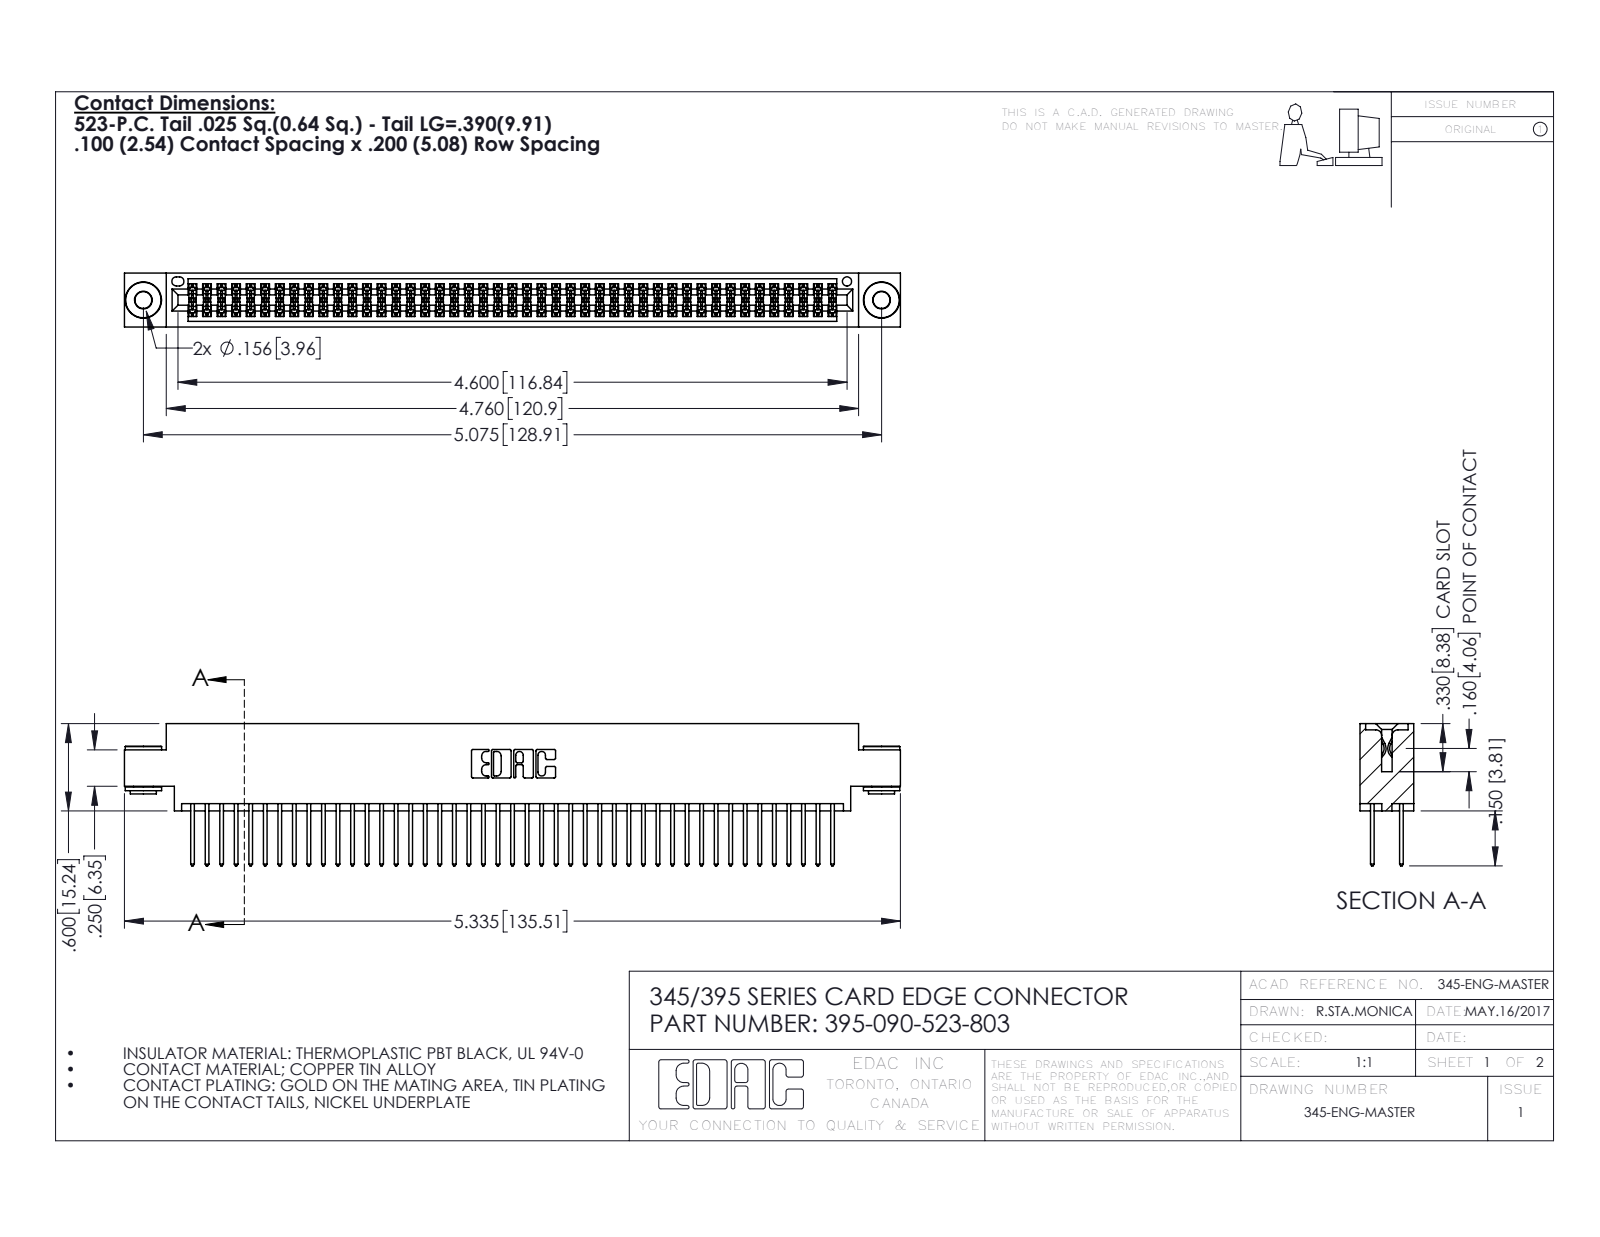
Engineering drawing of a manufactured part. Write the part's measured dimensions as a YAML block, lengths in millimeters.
part_name: "345-292-001_345-293-123; 345 Part_0.170 Offset - 0.156 Dia-TH; 395-090-523-803; 345-250-002_345-250-002-102"
step_written_by: "SolidWorks 2016 (CONFIG_CONTROL_DESIGN)"
units: millimeters
bodies: {solids: 93, faces: 4668, planar: 3064, cylindrical: 1596, other: 8}
overall_size: [135.5, 24.8, 9.4]
volume: 13300
surface_area: 20860
round_holes:
  - {diameter: 2.9, count: 2}
  - {diameter: 4, count: 2}
  - {diameter: 1.6, count: 1}
round_bosses_or_shafts:
  - {diameter: 6.4, count: 2}
  - {diameter: 4.6, count: 2}
  - {diameter: 3.5, count: 2}
partial_cylinders:
  - {radius: 0.2, count: 135}
  - {radius: 0.3, count: 90}
  - {radius: 0.3, count: 22}
  - {radius: 0.2, count: 6}
  - {radius: 0.8, count: 6}
  - {radius: 0.7, count: 3}
  - {radius: 0.4, count: 2}
  - {radius: 0.5, count: 2}
face_to_face_distances: [1.8, 7.6, 5.1, 2.5, 6.9, 0.6, 9.4, 5.7, 4.4, 3.8]
hole_center_spacings: [6.9, 122.9, 128.9]
